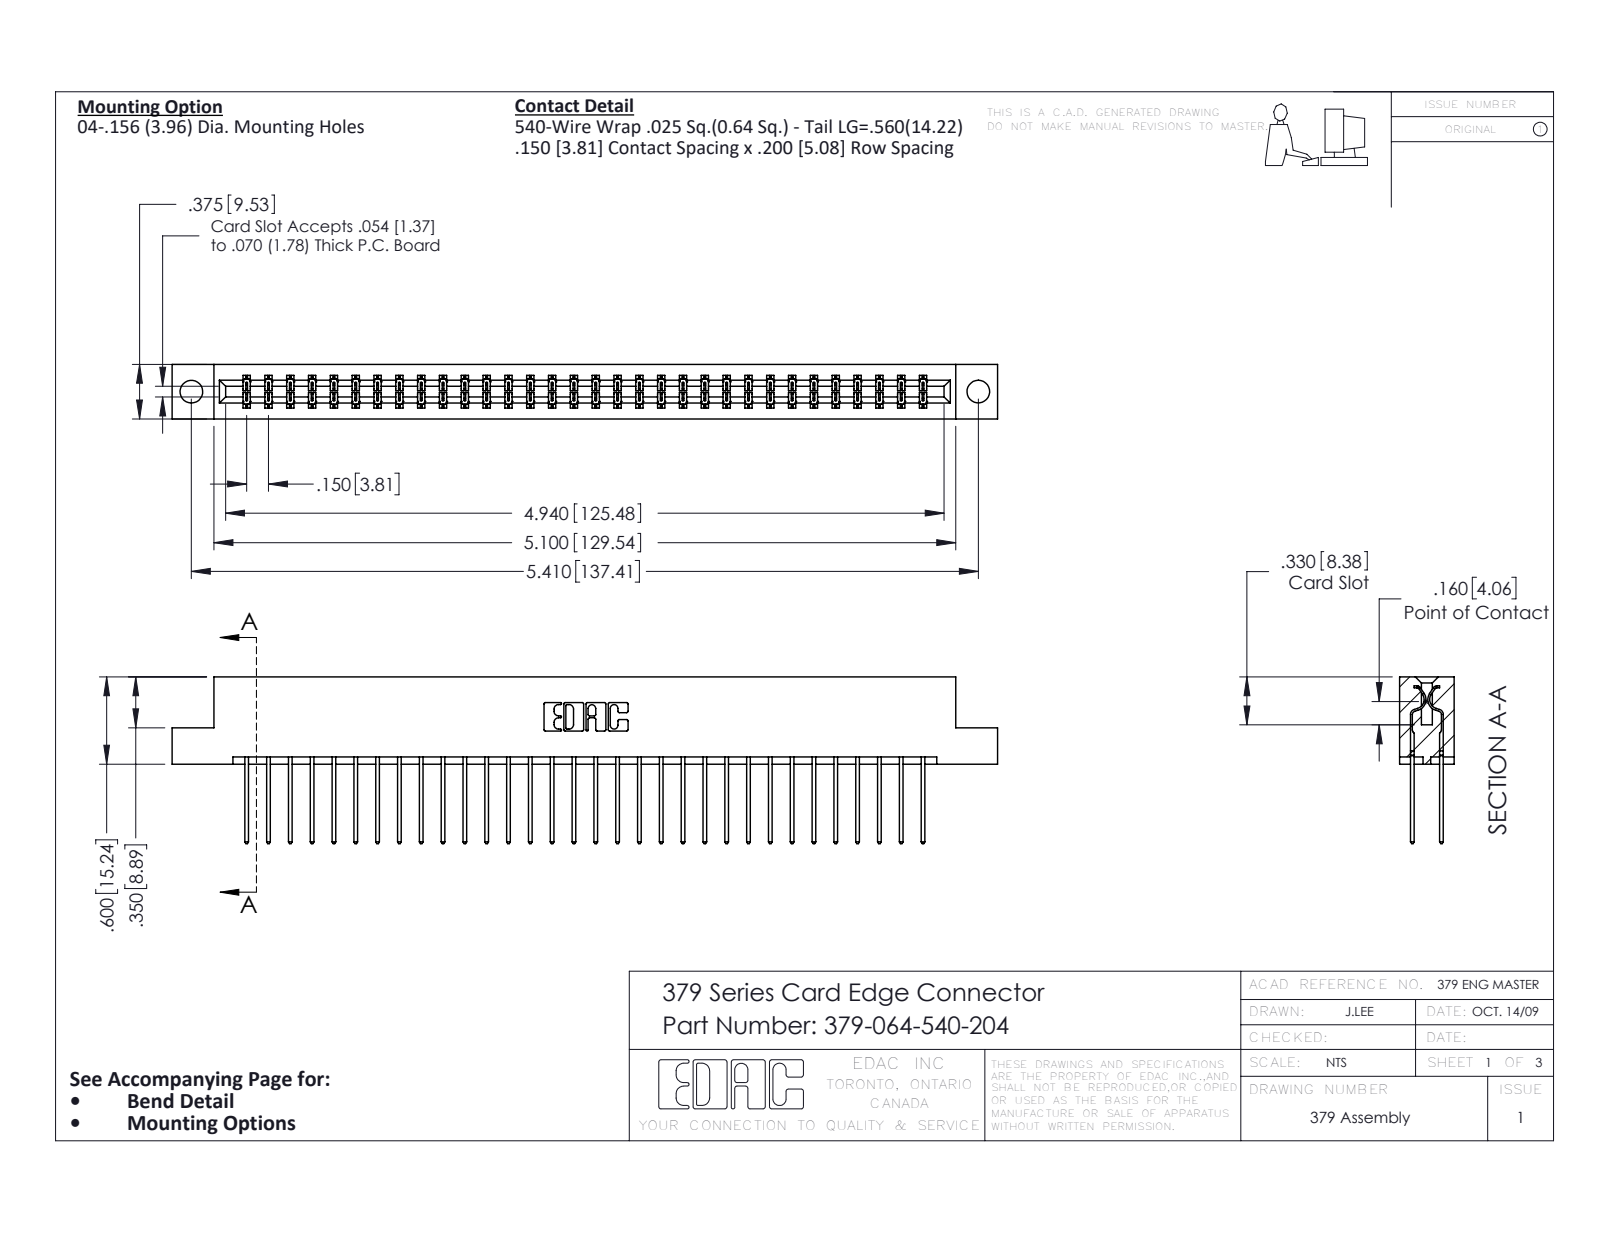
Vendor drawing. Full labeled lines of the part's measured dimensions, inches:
Part name (STEP PRODUCT): 379 Part_Flush - .156 Dia - TH; 379-064-540-204; 345-292-001_345-293-140
STEP written by: SolidWorks 2016 (CONFIG_CONTROL_DESIGN)
Units: inches
Bodies: 65 solids, 3442 faces (2374 planar, 1068 cylindrical, 0 other)
Overall size (bounding box): 5.675 × 1.147 × 0.375
Volume: 0.939 in³ · Surface area: 28.2 in²
Round holes (diameter × count): ⌀0.156 ×2
Partial cylindrical surfaces — rounded edges, fillets, slot ends (radius × count): R0.006 ×96, R0.01 ×64, R0.01 ×22, R0.007 ×6, R0.031 ×6, R0.026 ×3, R0.014 ×2, R0.022 ×2
Main face-to-face distances: 0.3, 0.075, 0.375, 0.2, 0.1, 0.275, 0.025, 0.15, 0.076, 0.225
Hole centre spacings: 5.41
